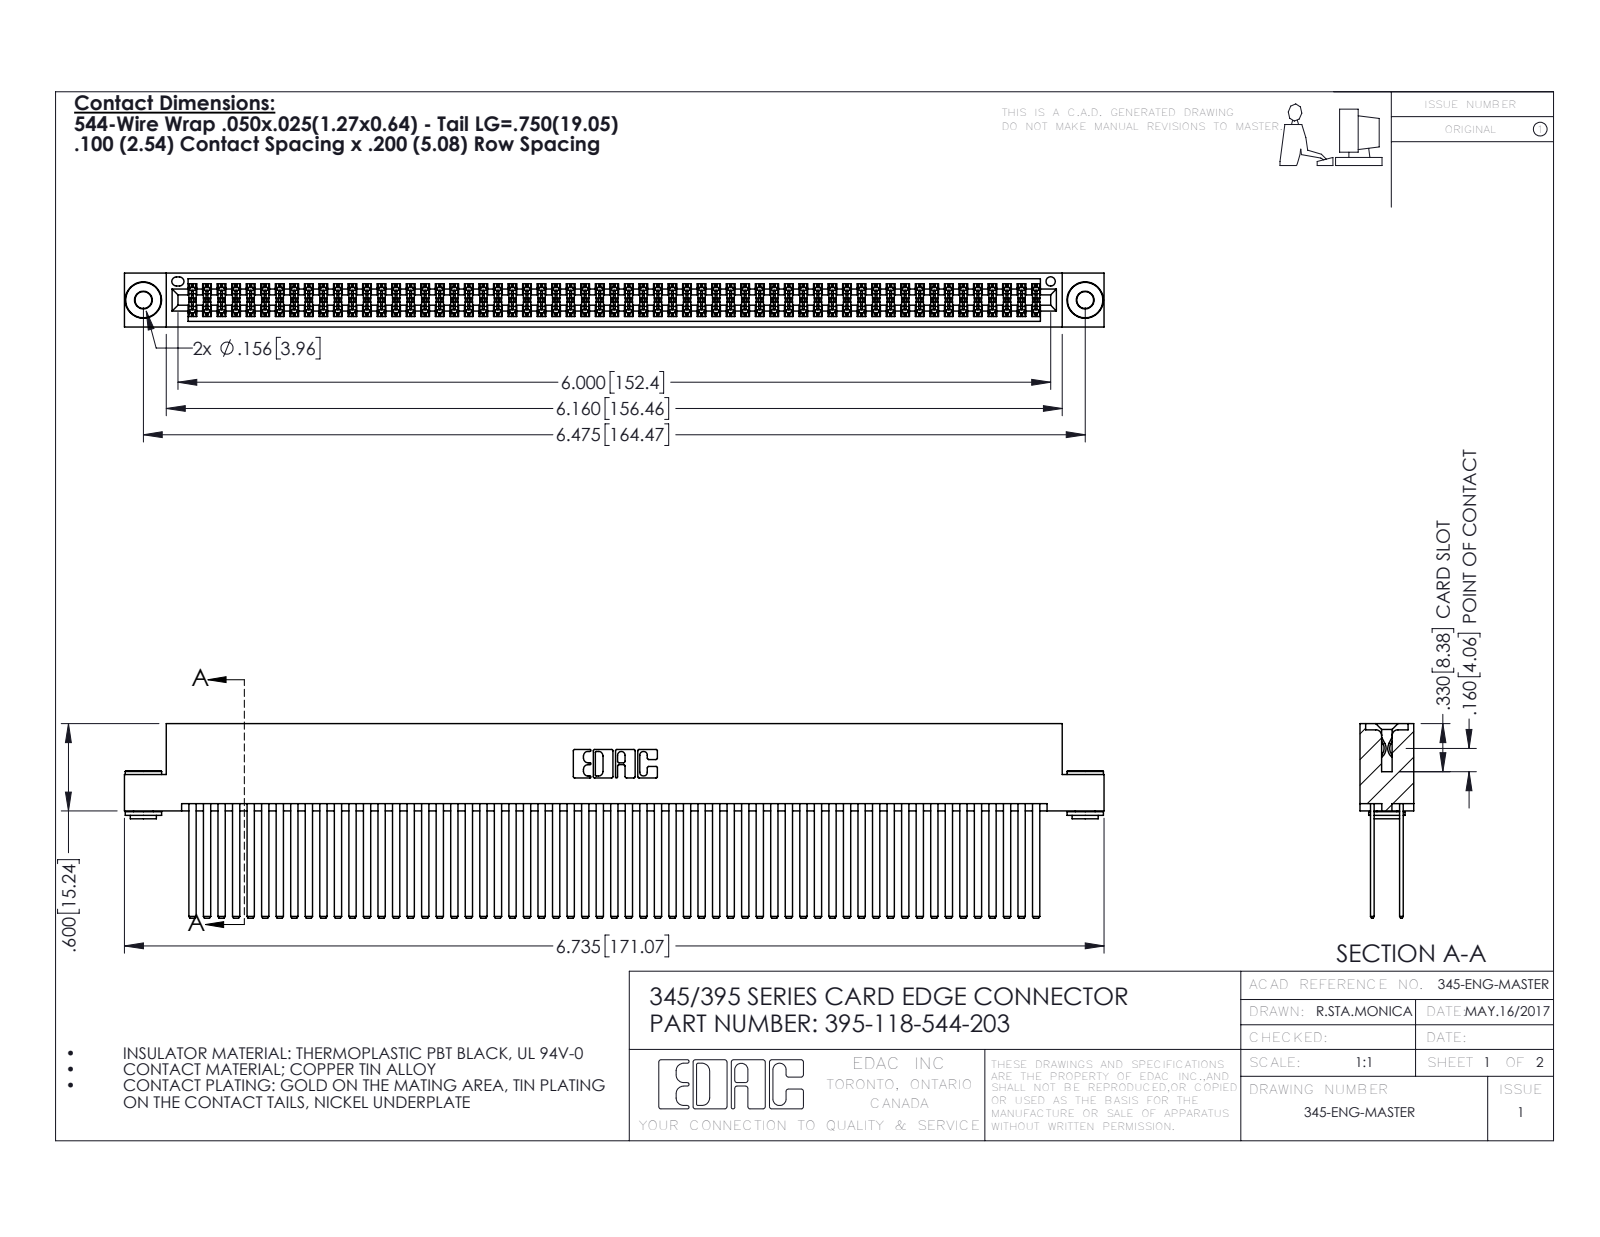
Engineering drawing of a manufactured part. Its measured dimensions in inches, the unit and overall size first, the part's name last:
Units: inches
Overall size (bounding box): 6.735 × 1.337 × 0.37
Round holes (diameter × count): ⌀0.116 ×2, ⌀0.156 ×2, ⌀0.064 ×1
Round bosses / shafts (diameter × count): ⌀0.25 ×2, ⌀0.18 ×2, ⌀0.136 ×2
Partial cylindrical surfaces — rounded edges, fillets, slot ends (radius × count): R0.006 ×177, R0.01 ×22, R0.007 ×6, R0.031 ×6, R0.026 ×3, R0.014 ×2, R0.019 ×2, R0.022 ×2
Main face-to-face distances: 0.2, 0.025, 0.072, 0.098, 0.272, 0.298, 0.225, 0.175, 0.37, 0.05
Hole centre spacings: 0.27, 6.239, 6.475
Volume: 1.126 in³ · Surface area: 50.61 in²
Bodies: 121 solids, 5356 faces (3512 planar, 1836 cylindrical, 8 other)
Part name (STEP PRODUCT): 395-118-544-203; 345-292-001_345-293-144; 345 Part_Flush Mounting Lugs - 0.156 Dia-TH; 345-250-002_345-250-002-102
STEP written by: SolidWorks 2016 (CONFIG_CONTROL_DESIGN)
